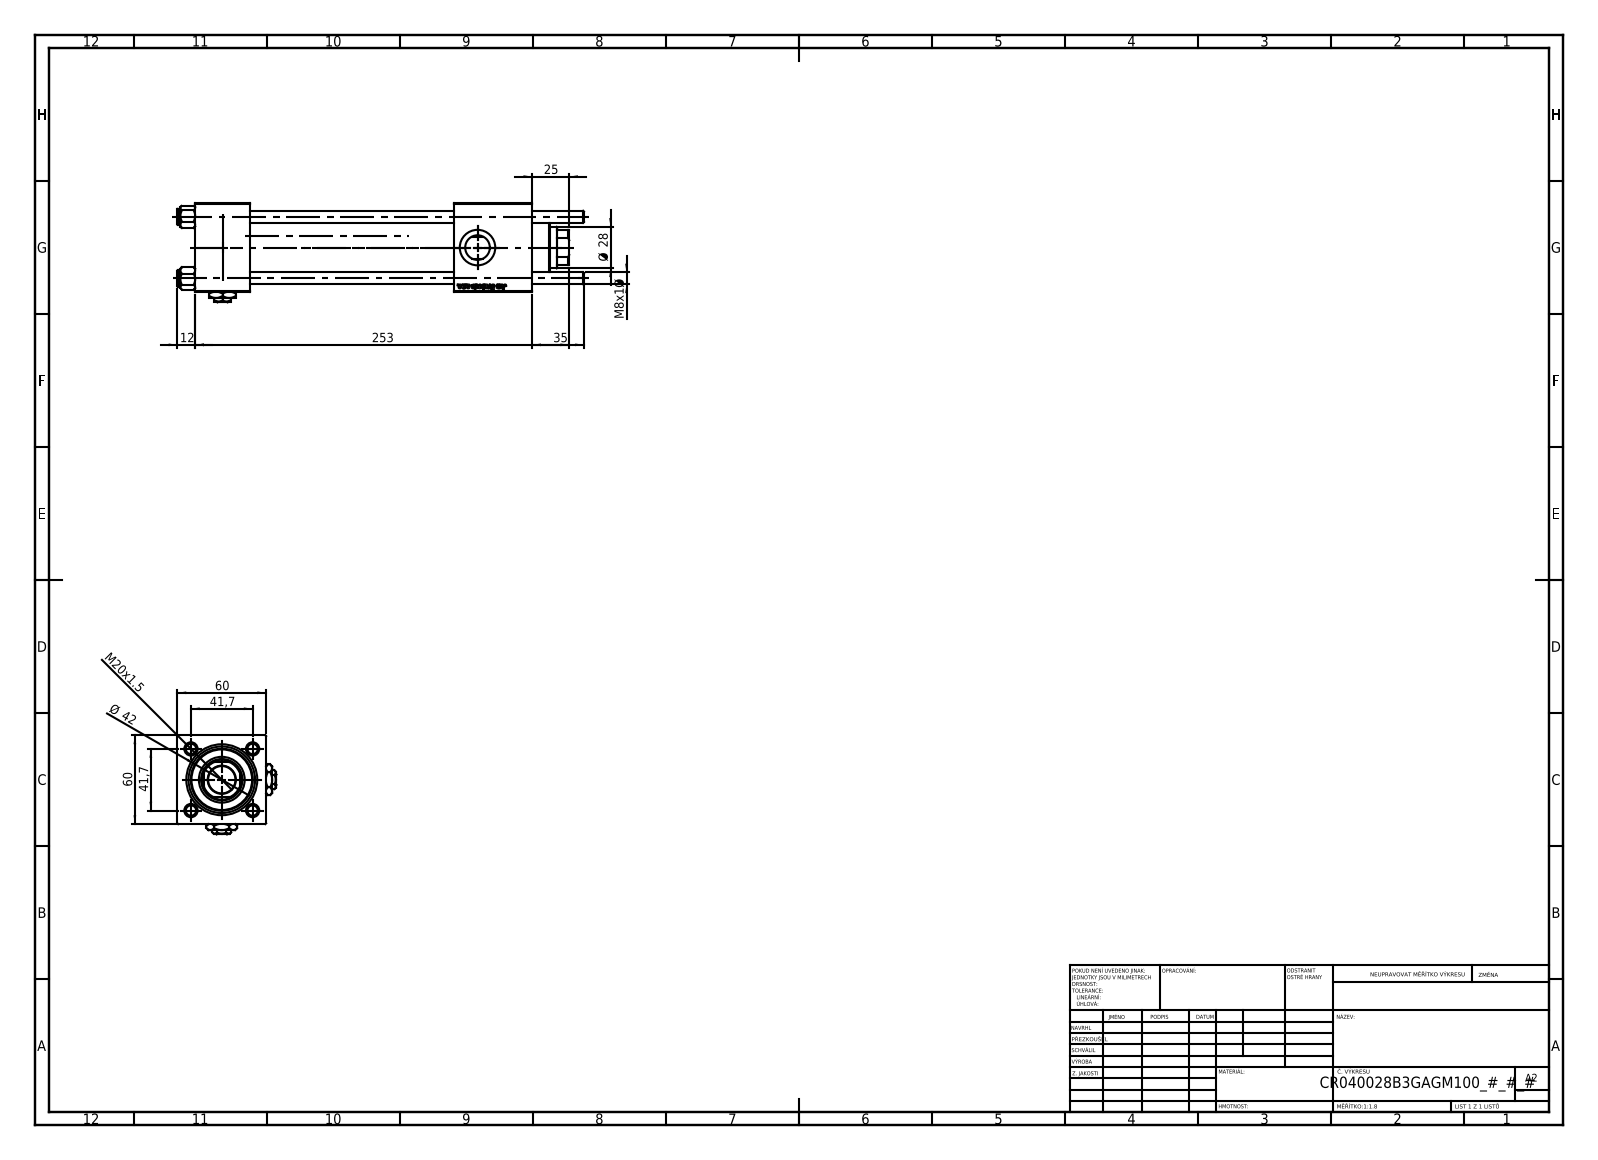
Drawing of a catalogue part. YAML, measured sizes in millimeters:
part_name: "V215CR_VCP_B; V215CR_B-1; Zatka_pro_OIL_PORT; V215CR_B_TYCINKA (+2 more)"
step_written_by: "SolidWorks 2019 (CONFIG_CONTROL_DESIGN)"
units: millimeters
bodies: {solids: 13, faces: 1260, planar: 480, cylindrical: 90, other: 690}
overall_size: [275, 67, 67]
volume: 529393
surface_area: 159668
round_holes:
  - {diameter: 8, count: 4}
  - {diameter: 7, count: 2}
  - {diameter: 16.66, count: 2}
  - {diameter: 24, count: 2}
  - {diameter: 16, count: 1}
  - {diameter: 18.5, count: 1}
  - {diameter: 28, count: 1}
  - {diameter: 31, count: 1}
  - {diameter: 40, count: 1}
  - {diameter: 45, count: 1}
round_bosses_or_shafts:
  - {diameter: 11, count: 4}
  - {diameter: 46, count: 1}
  - {diameter: 42, count: 1}
partial_cylinders:
  - {radius: 13.5, count: 1}
face_to_face_distances: [60, 37, 175, 138, 53, 199.3, 162.3, 24.3, 228, 191]
hole_center_spacings: [29.49, 41.7, 58.97]
